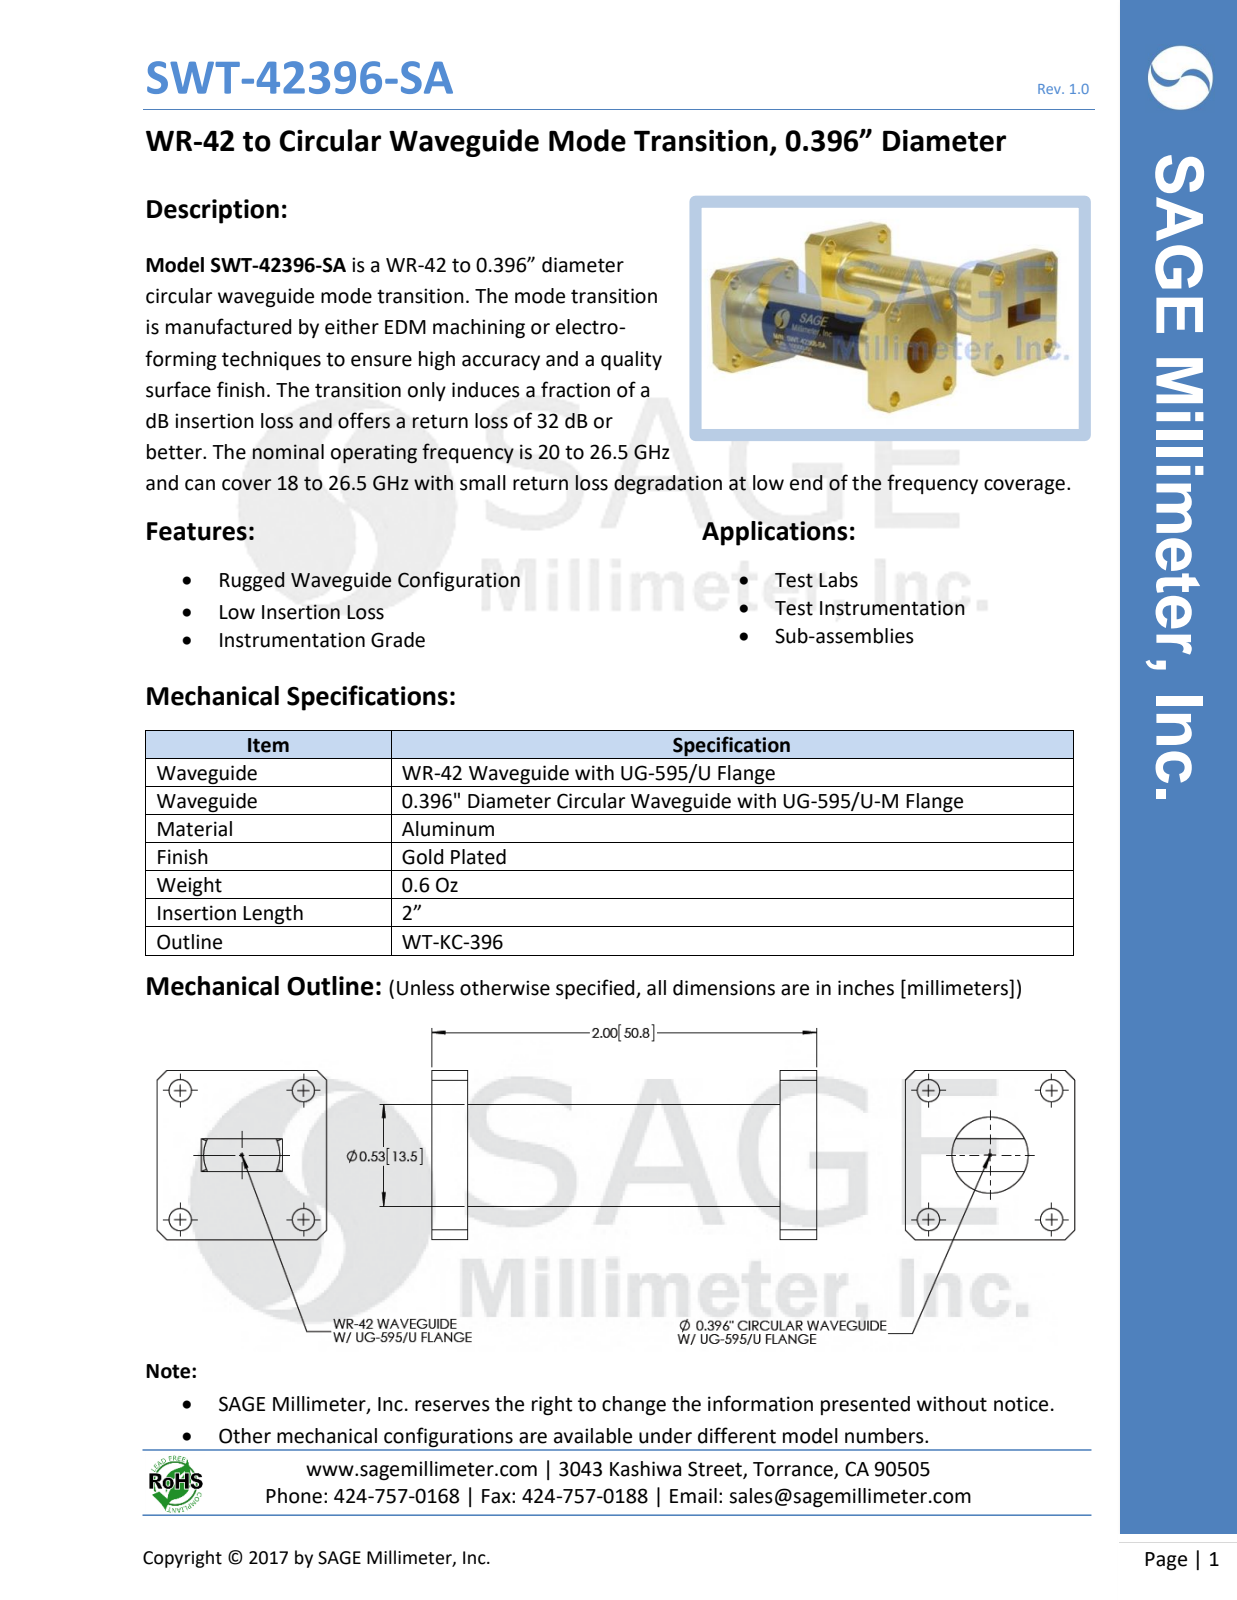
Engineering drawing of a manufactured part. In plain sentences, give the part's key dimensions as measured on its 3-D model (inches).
The part is named "DMWT-42-401-C, DF". Its 3-D file was written by "SolidWorks 2016 (CONFIG_CONTROL_DESIGN)". It is 1 solid with 78 faces: 58 planar, 20 cylindrical and 0 other. Overall it measures 2 by 0.88 by 0.88 inches. Its volume is 0.631 cubic inches and its surface area 6.956 square inches. Round holes: 4 of diameter 0.116, 1 of diameter 0.396. Round bosses or shafts: 1 of diameter 0.53. The main face-to-face distances are 0.19, 1.81, 2, 0.88, 1.62, 1.99, 0.18, 1.8, 1.98, 1.173. The hole center spacings are 0.463, 0.64, 0.67, 0.927.
